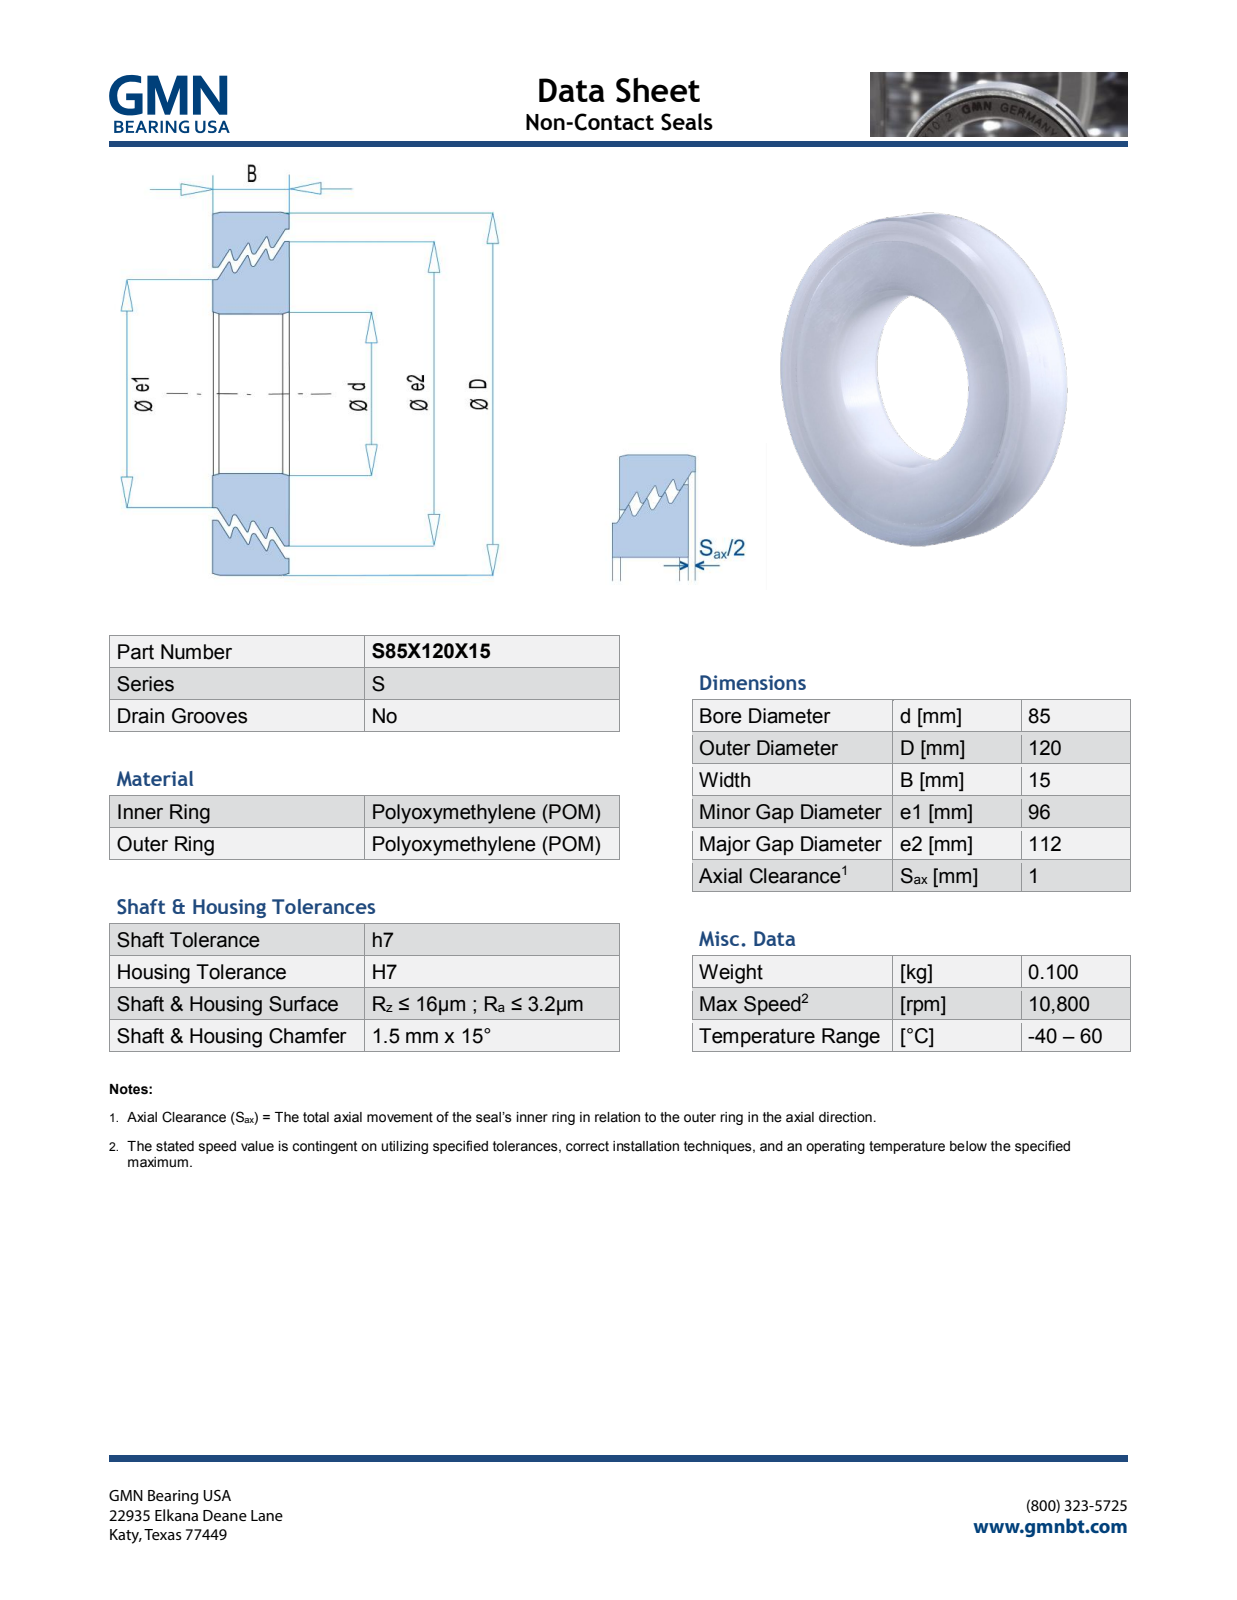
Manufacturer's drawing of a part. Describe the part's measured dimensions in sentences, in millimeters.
The part is named "S85X120X15_PRT". Its 3-D file was written by "PRO/ENGINEER BY PARAMETRIC TECHNOLOGY CORPORATION, 2013150 (AUTOMOTIVE_DESIGN)". It is 2 solids with 697 faces: 601 planar, 12 cylindrical and 84 other. Overall it measures 120 by 120 by 15.07 millimeters. Its volume is 79 015 cubic millimeters and its surface area 37 842 square millimeters. Round holes: 1 of diameter 85, 1 of diameter 97.63, 1 of diameter 113.63. Round bosses or shafts: 1 of diameter 120, 1 of diameter 112, 1 of diameter 96. The main face-to-face distances are 15, 15.07, 0.36, 2.53, 2.89, 0.37, 2.9, 0.31, 2.05, 2.17.
